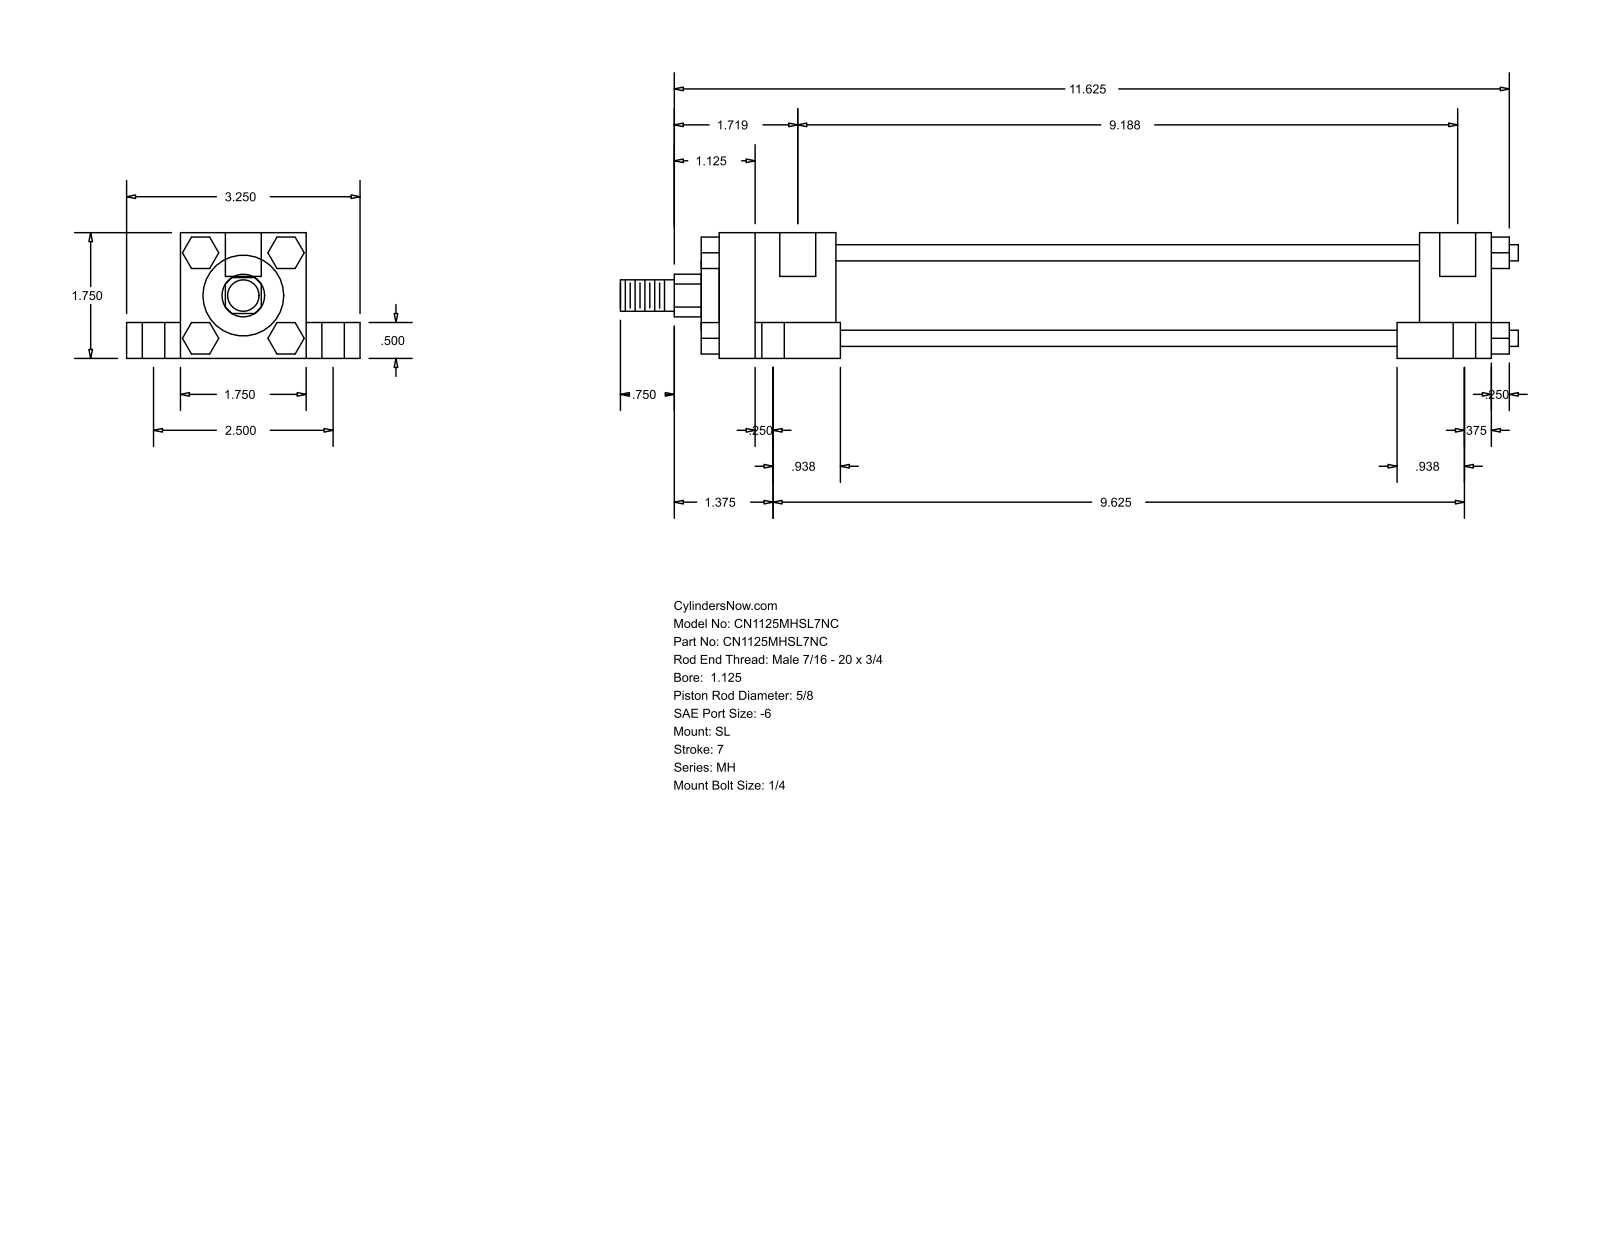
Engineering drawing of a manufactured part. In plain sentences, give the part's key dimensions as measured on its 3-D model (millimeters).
The part is named "MH_SL__0112_0.625". Its 3-D file was written by "GSSL Pune (CONFIG_CONTROL_DESIGN)". It is 0 solids with 150 faces: 114 planar, 36 cylindrical and 0 other. Overall it measures 317.5 by 82.55 by 44.45 millimeters. Round holes: 4 of diameter 5.56, 4 of diameter 7.94, 4 of diameter 14.29, 2 of diameter 12.7. Round bosses or shafts: 4 of diameter 5.71, 1 of diameter 34.92, 1 of diameter 28.57, 1 of diameter 15.88, 1 of diameter 11.11. Partial cylindrical surfaces (rounded edges, fillets, slot ends): 1 of radius 7.54. The main face-to-face distances are 44.46, 19.04, 12.7, 31.76, 63.5, 11.11, 47.62, 33.34, 227.02, 206.37. The hole center spacings are 31.84, 32.23, 32.93, 63.5, 230.19, 234.73, 237.87, 241.02.
